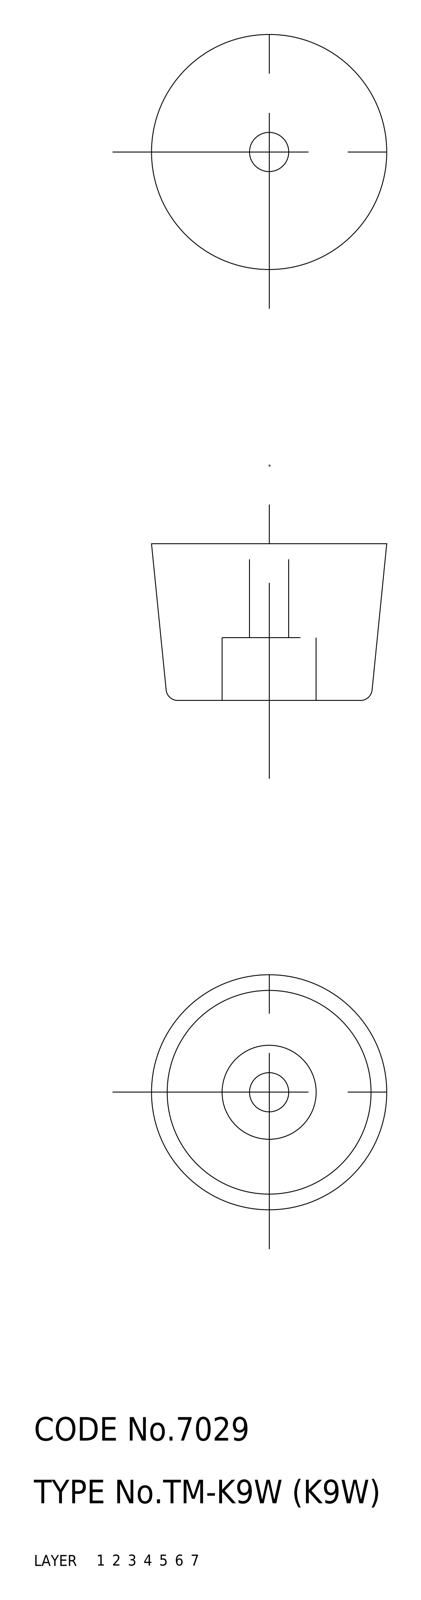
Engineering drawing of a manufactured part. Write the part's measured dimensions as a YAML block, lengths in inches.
part_name: "washer; rubber foot; K9W_6786_36"
step_written_by: "CADfix (AUTOMOTIVE_DESIGN)"
units: inches
bodies: {solids: 2, faces: 23, planar: 0, cylindrical: 0, other: 23}
overall_size: [1.181, 1.181, 0.787]
volume: 0.683
surface_area: 5.947
